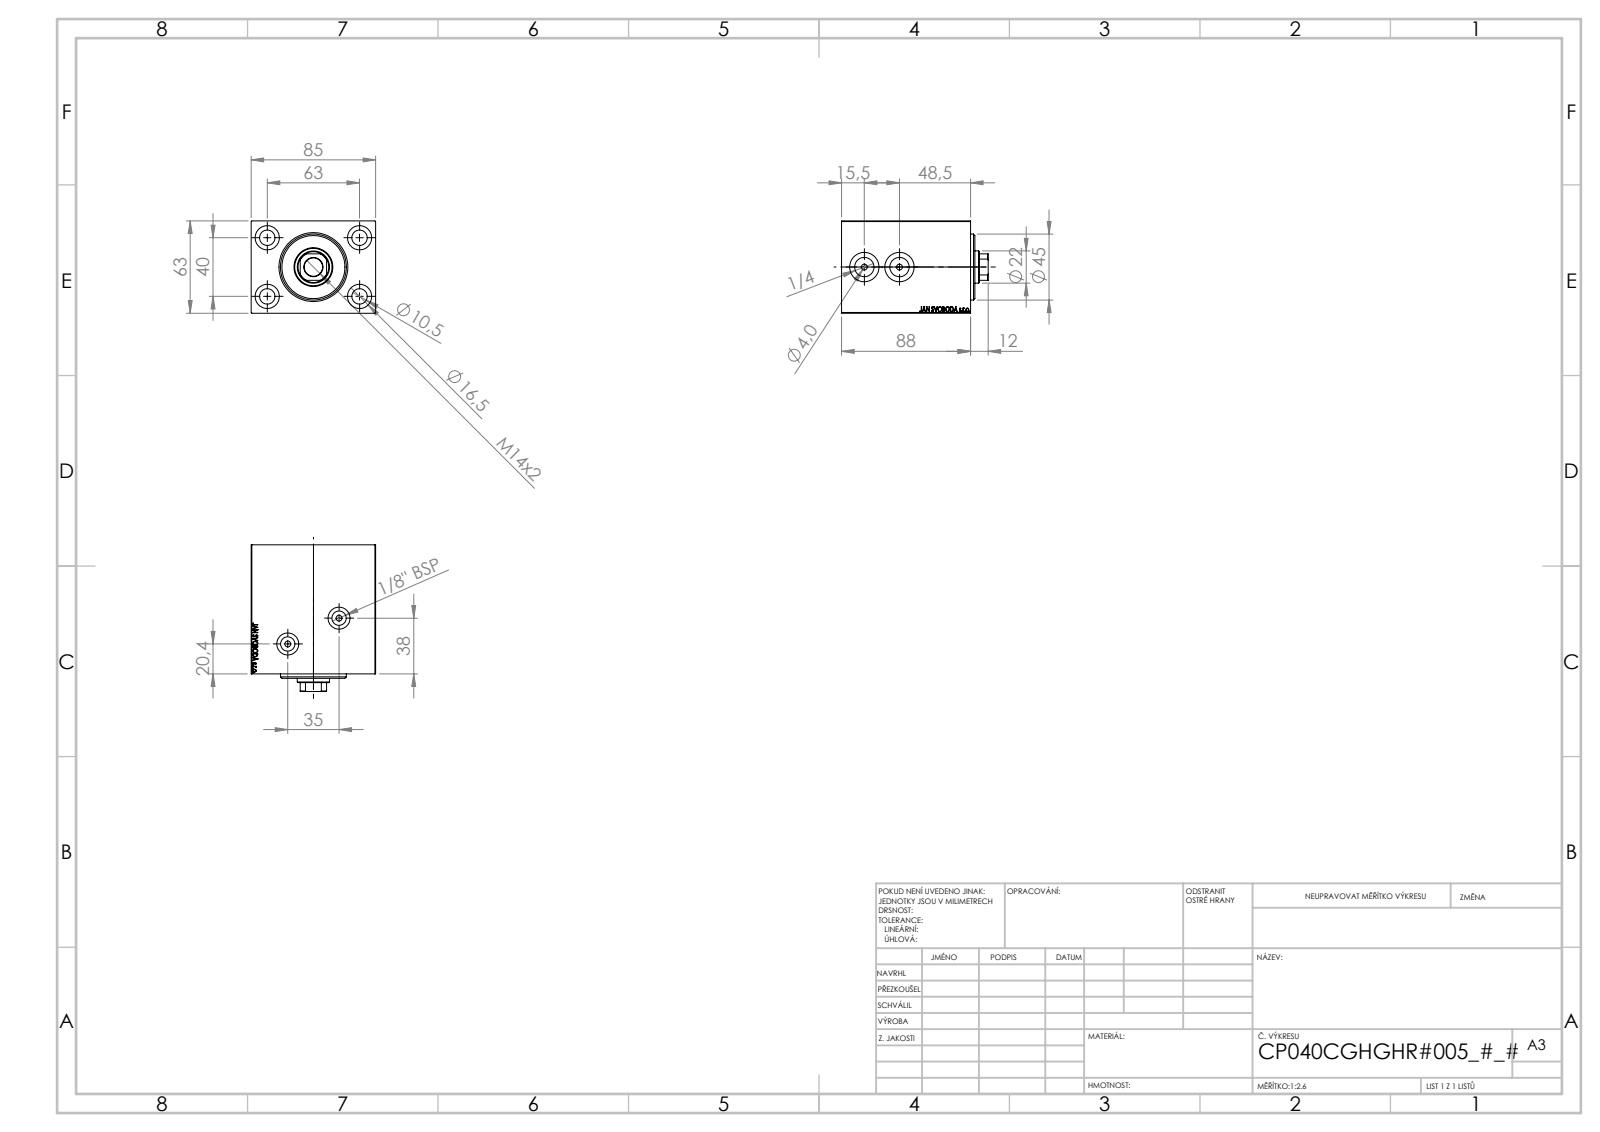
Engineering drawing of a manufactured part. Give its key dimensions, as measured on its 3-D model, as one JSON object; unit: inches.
{"part_name": "V450CP_C; V450CP_B_VCP; V450CP_VC_B", "step_written_by": "SolidWorks 2019 (CONFIG_CONTROL_DESIGN)", "units": "inches", "bodies": {"solids": 3, "faces": 885, "planar": 413, "cylindrical": 74, "other": 398}, "overall_size": [3.937, 3.346, 2.48], "volume_in3": 25.92, "surface_area_in2": 129.1, "round_holes": [[0.157, 4], [0.413, 4], [0.65, 4], [0.383, 2], [0.518, 2], [0.591, 2], [0.787, 2], [0.492, 1], [0.866, 1], [1.004, 1], [1.043, 1], [1.575, 1]], "partial_cylinders_radius": [[0.413, 1]], "face_to_face_distances": [2.48, 3.346, 3.465, 0.472, 2.992, 1.378, 1.614, 1.181, 0.197, 1.85], "hole_center_spacings": [1.469, 1.575, 2.48, 2.938, 0.945, 1.543]}
